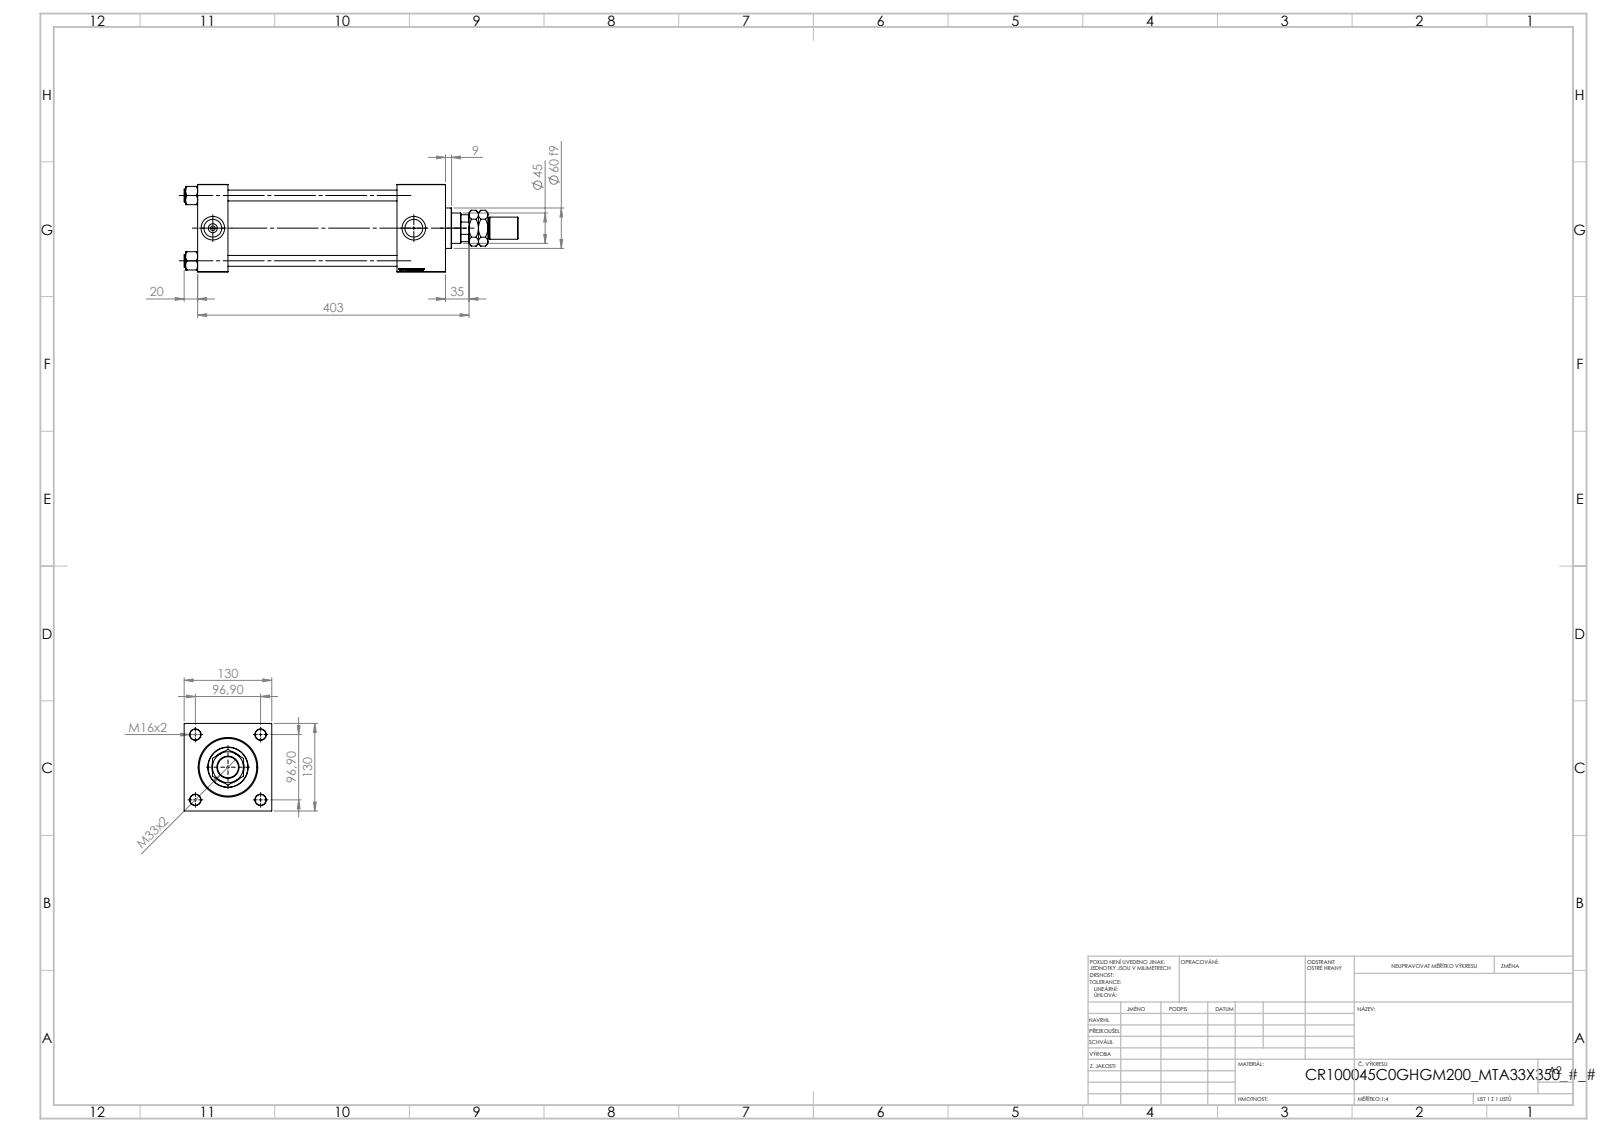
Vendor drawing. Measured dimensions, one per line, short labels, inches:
name: MTA; NUT_M5_C; V215CR_C_TYCINKA; V215CR_VCP_C (+2 more)
written by: SolidWorks 2019 (CONFIG_CONTROL_DESIGN)
unit: in
bodies: 12 solids, 1245 faces (589 planar, 90 cylindrical, 566 other)
size: 19.528 × 5.118 × 5.118
volume: 190.4 in³; area: 801.6 in²
holes: 4× ⌀0.63, 2× ⌀0.276, 2× ⌀1.041, 2× ⌀1.378, 1× ⌀1.24, 1× ⌀1.772, 1× ⌀1.89, 1× ⌀2.992, 1× ⌀3.366, 1× ⌀3.937
bosses: 4× ⌀0.748, 1× ⌀4.173, 1× ⌀2.362, 1× ⌀1.299, 1× ⌀1.22
rounds: 1× R0.866
face distances: 5.118, 1.772, 14.488, 12.717, 11.654, 9.882, 2.835, 3.78, 2.008, 7.874
hole spacings: 2.698, 3.815, 5.395, 11.752
